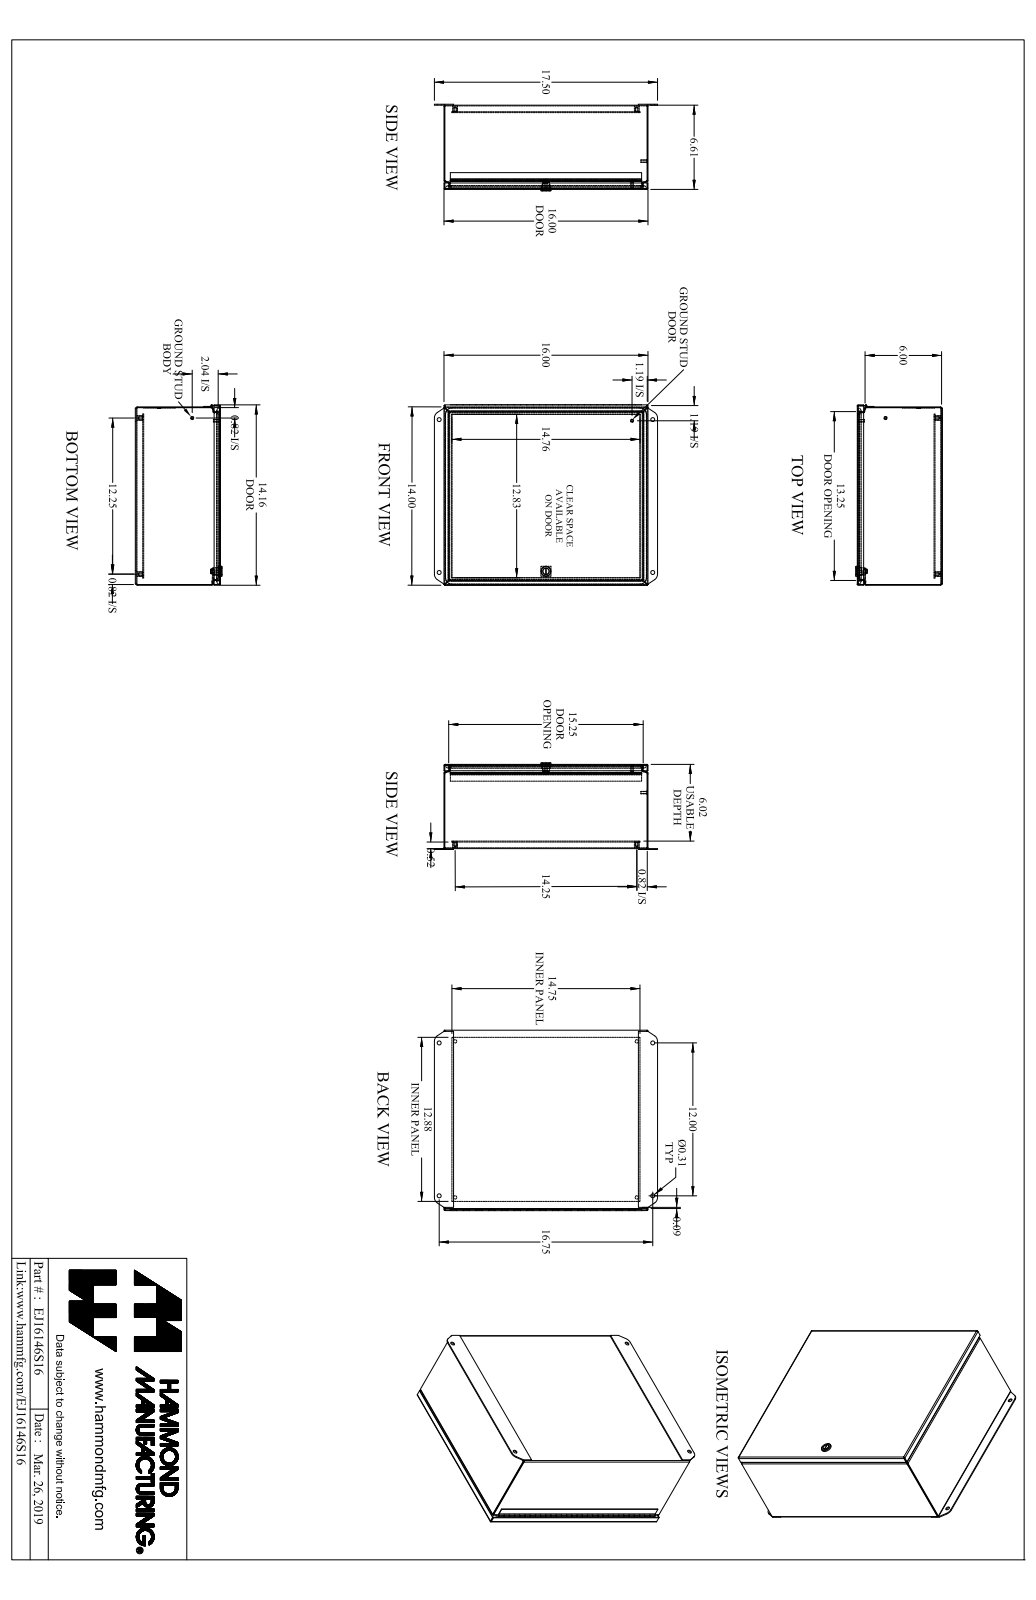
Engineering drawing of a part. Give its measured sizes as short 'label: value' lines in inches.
name: EJ16146S16_Default
written by: SolidWorks 2019 (CONFIG_CONTROL_DESIGN)
unit: in
bodies: 16 solids, 692 faces (358 planar, 254 cylindrical, 80 other)
size: 17.5 × 14.165 × 6.805
volume: 72.82 in³; area: 2 401 in²
holes: 4× ⌀0.156, 4× ⌀0.265, 4× ⌀0.313, 1× ⌀0.05, 1× ⌀0.516
bosses: 4× ⌀0.375, 2× ⌀0.25, 2× ⌀0.19, 1× ⌀0.788, 1× ⌀0.535, 1× ⌀0.496, 1× ⌀0.435, 1× ⌀0.1
rounds: 16× R0.029, 16× R0.086, 12× R0.281, 4× R0.25, 4× R0.499, 4× R0.5, 2× R0.06, 1× R0.03
face distances: 0.057, 6.554, 0.072, 0.589, 6.611, 6.497, 6.094, 6.037, 0.46, 0.517
hole spacings: 1.257, 12.189, 15.5, 19.679, 7.128, 8.376, 12, 12.25
